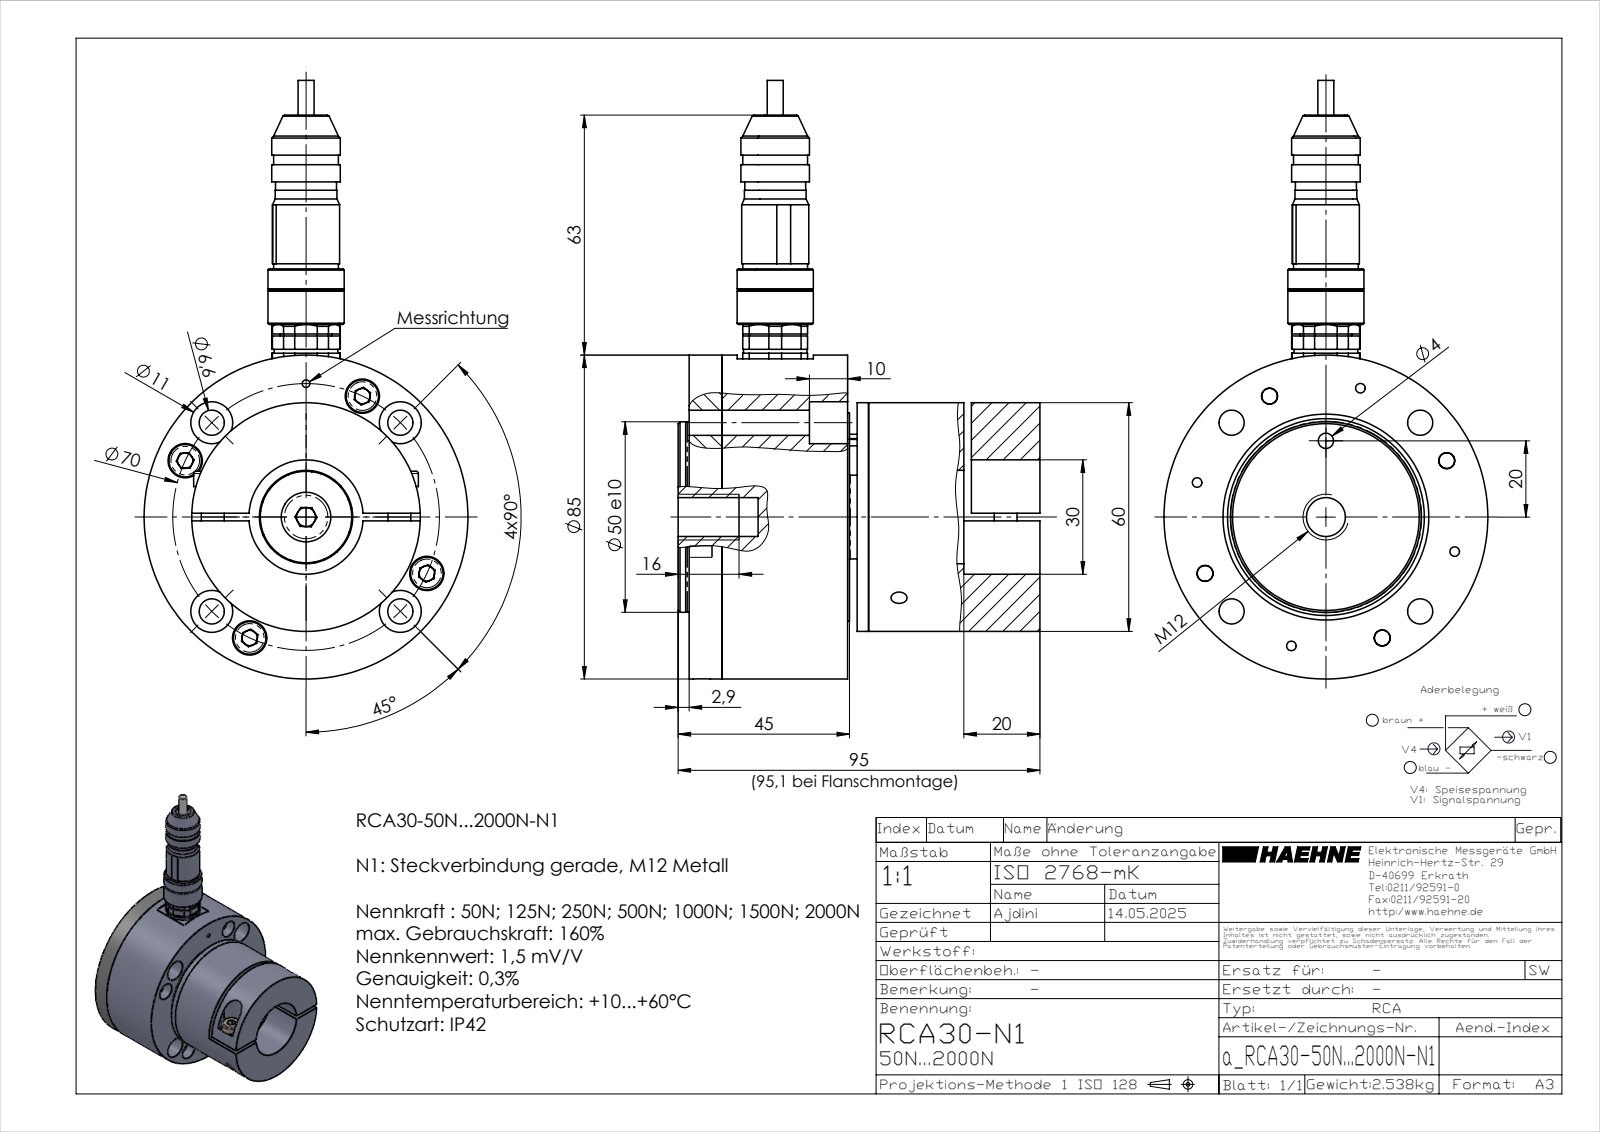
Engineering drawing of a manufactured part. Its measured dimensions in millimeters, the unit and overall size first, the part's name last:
Units: millimetres
Overall size (bounding box): 157.06 × 95.1 × 85
Round holes (diameter × count): ⌀3.4 ×9, ⌀2.5 ×8, ⌀6.6 ×6, ⌀1 ×5, ⌀4.2 ×5, ⌀4 ×4, ⌀5.3 ×4, ⌀9 ×4, ⌀11 ×4, ⌀4.5 ×2, ⌀5 ×2, ⌀2 ×1
Round bosses / shafts (diameter × count): ⌀3 ×9, ⌀5.7 ×8, ⌀8.5 ×4, ⌀5 ×4, ⌀1.5 ×4, ⌀1 ×4, ⌀17 ×2, ⌀10 ×2
Partial cylindrical surfaces — rounded edges, fillets, slot ends (radius × count): R0.3 ×6, R1 ×4, R5.5 ×2, R0.57 ×1, R0.6 ×1, R0.77 ×1, R3.5 ×1
Main face-to-face distances: 3, 2, 8.6, 47.1, 11.6, 45, 50, 30, 35.5, 38.5
Hole centre spacings: 35, 49.5, 24.78, 25.2, 32.8, 51.14, 56.46, 2.5
Volume: 369 591 mm³ · Surface area: 114 035 mm²
Bodies: 54 solids, 743 faces (377 planar, 203 cylindrical, 163 other)
Part name (STEP PRODUCT): a_RCA30-50N...2000N-N1; inafag_1203-tvh_7zkvytp7yxkimpdvw8sj0b5w4_26; inafag_1203-tvh_7zkvytp7yxkimpdvw8sj0b5w4_05; RCA30 Oberteil_30 (+8 more)
STEP written by: SolidWorks 2023 (AUTOMOTIVE_DESIGN)
